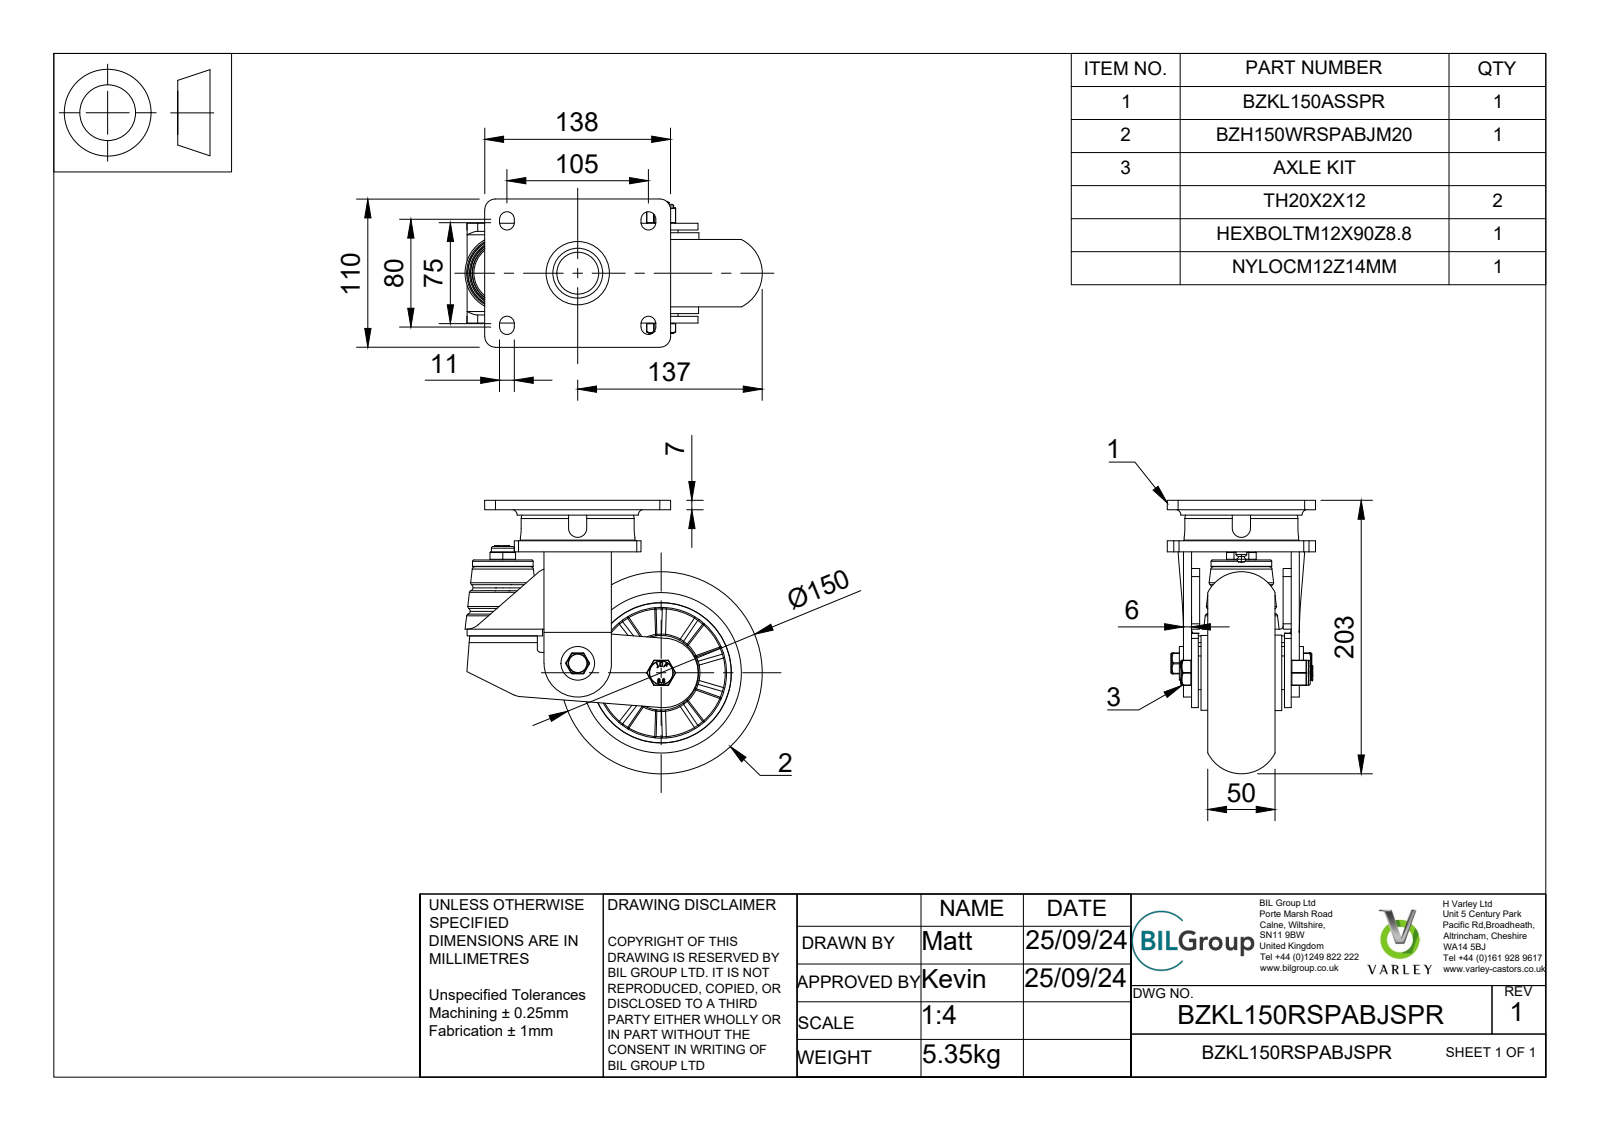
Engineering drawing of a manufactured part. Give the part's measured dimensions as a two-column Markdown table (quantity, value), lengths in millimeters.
| quantity | value |
| --- | --- |
| part name | BZKL150RSPABJSPR v3; BZKL150ASSPR v1; FABRICATED STEEL TOP PLATE (1); FABRICATED STEEL FORKS (1) (+8 more) |
| STEP written by | Autodesk Translation Framework v13.20.0.188 (AUTOMOTIVE_DESIGN) |
| units | millimeters |
| bodies | 50 solids, 1673 faces (527 planar, 435 cylindrical, 711 other) |
| overall size | 220.59 × 203 × 110 |
| volume | 1 174 000 mm³ |
| surface area | 358 095 mm² |
| round holes (diameter × count) | 12 × 2, 47 × 2, 10 × 1, 12.2 × 1, 12.75 × 1, 14 × 1, 20 × 1, 28.5 × 1, 30.8 × 1, 37 × 1, 40 × 1, 40.3 × 1 |
| round bosses / shafts (diameter × count) | 25 × 2, 11.83 × 2, 9.84 × 2, 85 × 1, 56 × 1, 55.5 × 1, 50 × 1, 45 × 1 |
| partial cylindrical surfaces (radius × count) | 0.5 × 37, 5.5 × 8, 0.75 × 6, 1 × 6, 4 × 5, 0.47 × 4, 0.9 × 4, 5 × 4 |
| main face-to-face distances | 5, 7, 6, 12, 74, 62, 69, 11, 13, 38.25 |
| hole center spacings | 55.57, 62.39 |
